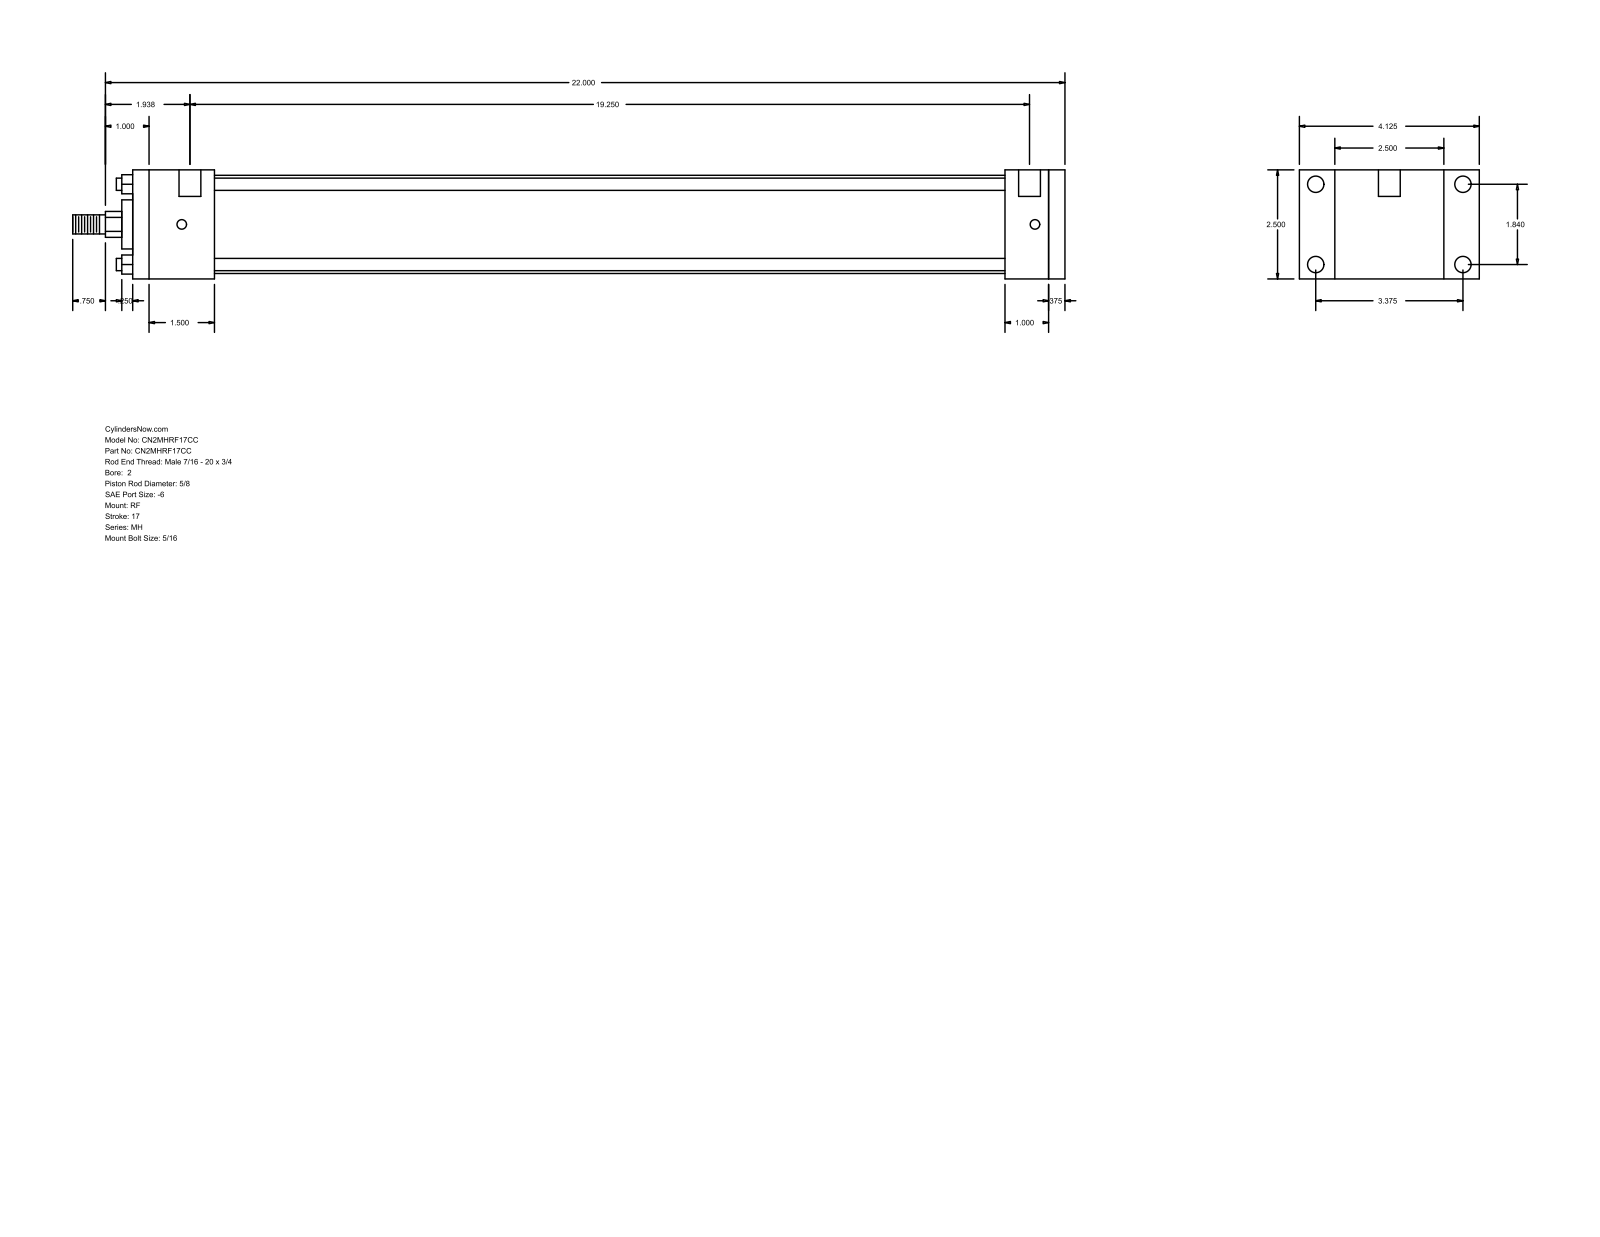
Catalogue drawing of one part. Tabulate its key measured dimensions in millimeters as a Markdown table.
| quantity | value |
| --- | --- |
| part name | MH_RF__0200_0.625 |
| STEP written by | GSSL Pune (CONFIG_CONTROL_DESIGN) |
| units | millimeters |
| bodies | 0 solids, 92 faces (64 planar, 28 cylindrical, 0 other) |
| overall size | 577.85 × 104.78 × 63.5 |
| round holes (diameter × count) | 5.56 × 4, 9.53 × 4, 12.7 × 2 |
| round bosses / shafts (diameter × count) | 7.14 × 4, 57.15 × 1, 28.57 × 1, 15.88 × 1, 11.11 × 1 |
| partial cylindrical surfaces (radius × count) | 7.54 × 1 |
| main face-to-face distances | 63.5, 542.92, 9.53, 533.39, 47.62, 508, 460.38, 485.77, 495.3, 25.39 |
| hole center spacings | 46.74, 85.72, 97.63, 496.89, 3.18, 4.76, 488.95, 492.13 |
